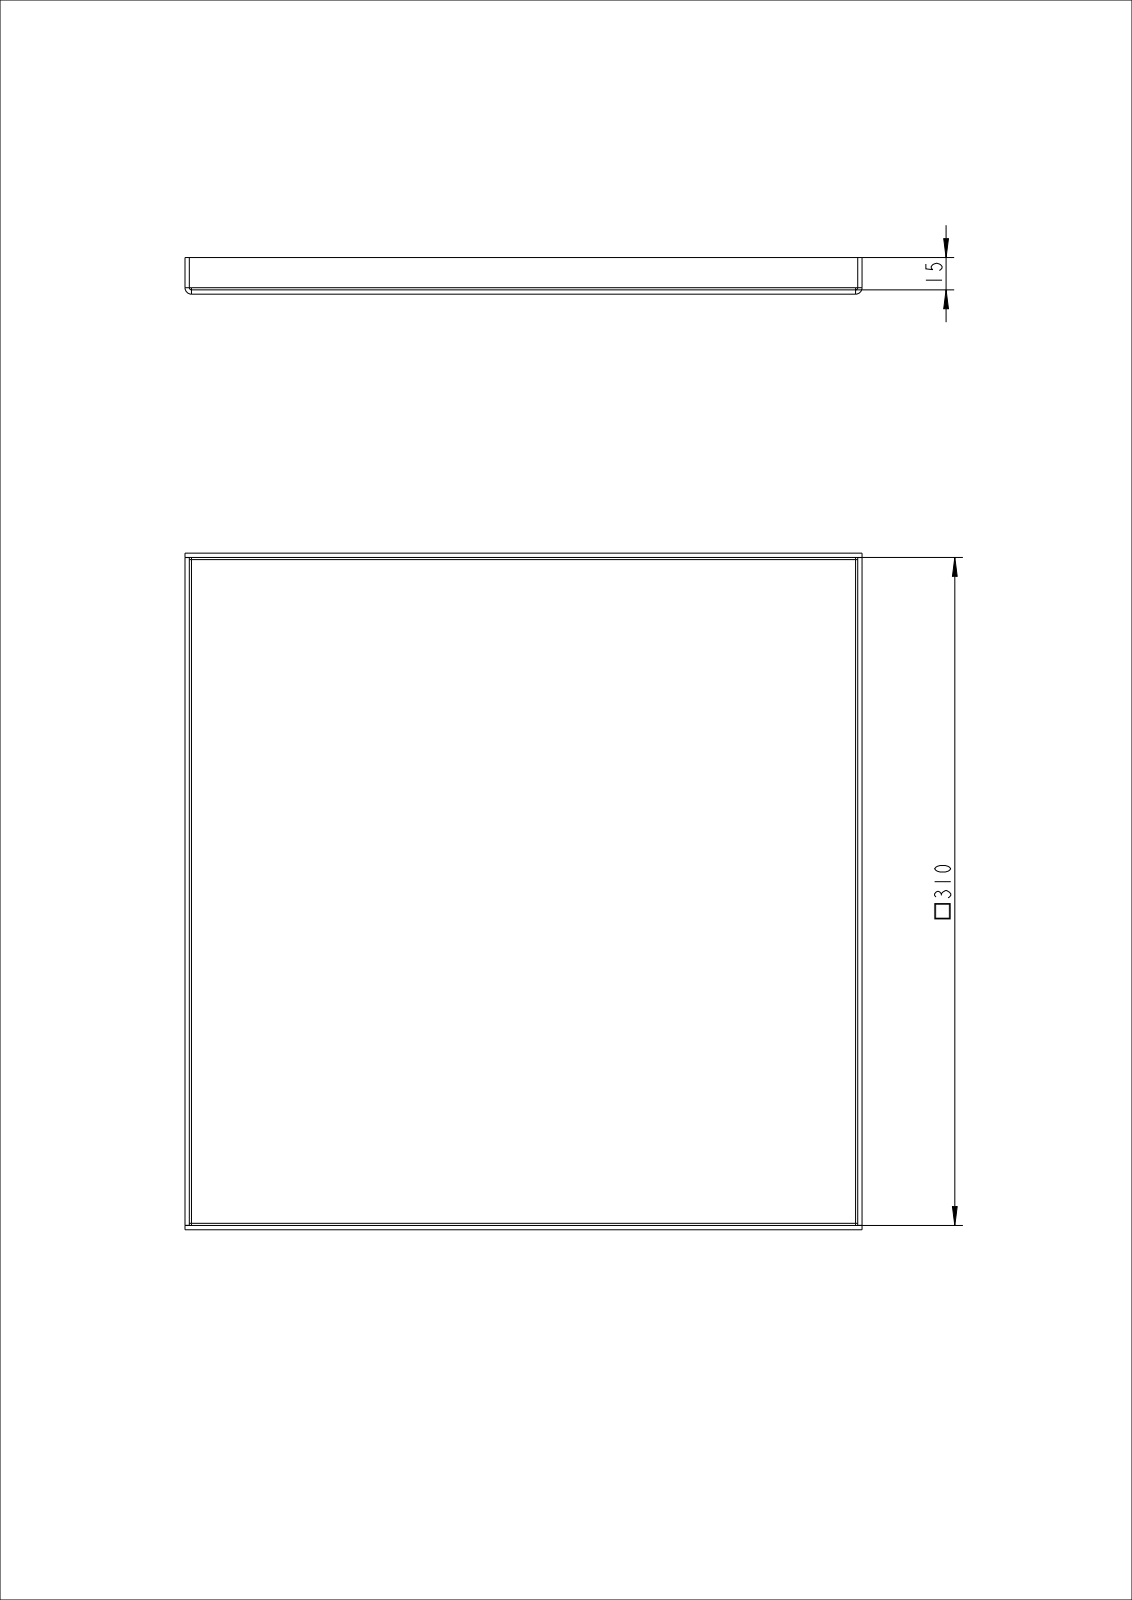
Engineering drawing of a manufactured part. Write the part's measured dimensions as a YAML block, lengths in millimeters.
part_name: "T-00649; T-00880_ASM; T-00886_ASM"
step_written_by: "CREO PARAMETRIC BY PTC INC, 2022024 (AUTOMOTIVE_DESIGN)"
units: millimeters
bodies: {solids: 1, faces: 46, planar: 38, cylindrical: 8, other: 0}
overall_size: [314, 314, 17]
volume: 232407
surface_area: 235209
partial_cylinders:
  - {radius: 1, count: 4}
  - {radius: 3, count: 4}
face_to_face_distances: [2, 312, 314, 310, 17, 15, 2.05, 311.95, 309.95, 3]
